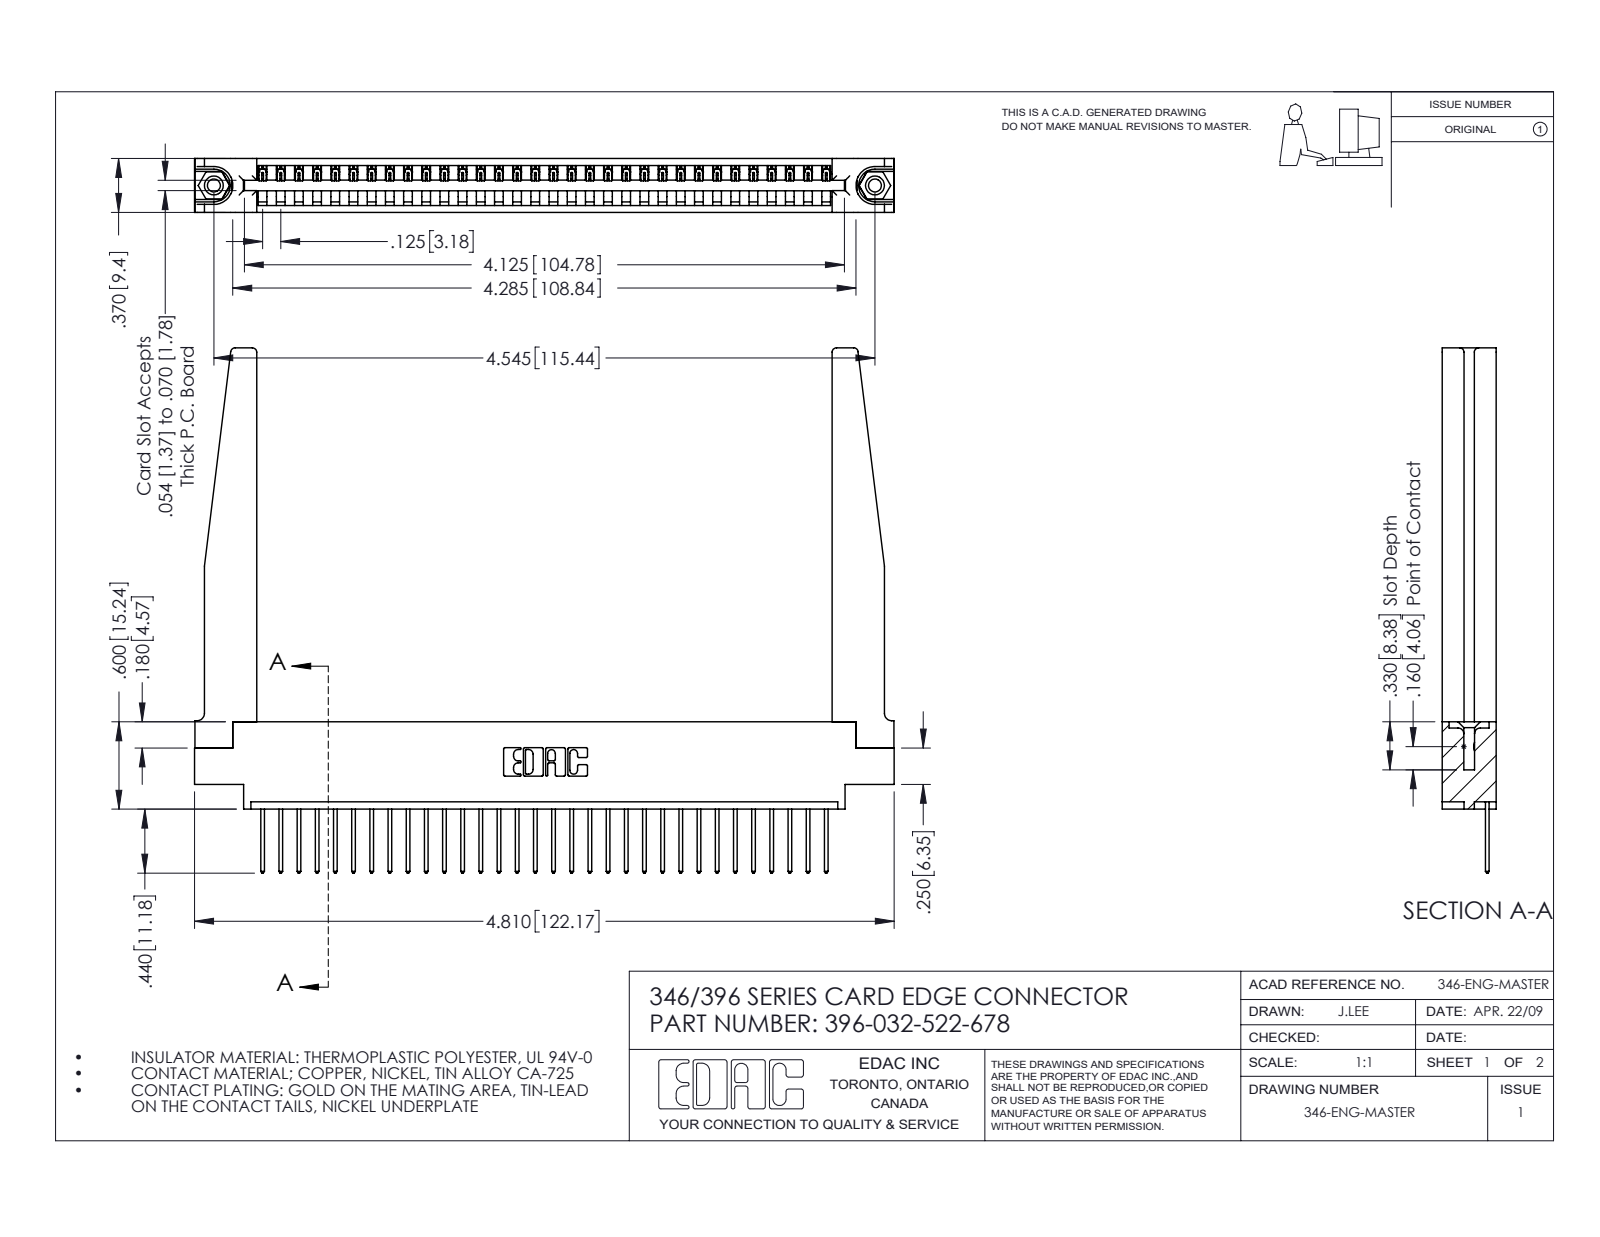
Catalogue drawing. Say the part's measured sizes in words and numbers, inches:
The part is named "396-032-522-678; 346-220-078_345-220-078; 345-250-001_345-250-001-102; 345-292-001_345-293-122 (+1 more)". Its 3-D file was written by "SolidWorks 2016 (CONFIG_CONTROL_DESIGN)". It is 37 solids with 2216 faces: 1502 planar, 662 cylindrical and 52 other. Overall it measures 4.81 by 3.61 by 0.37 inches. Its volume is 1.122 cubic inches and its surface area 32.63 square inches. Round holes: 2 of diameter 0.089, 2 of diameter 0.125, 2 of diameter 0.156, 1 of diameter 0.064. Round bosses or shafts: 2 of diameter 0.155. Partial cylindrical surfaces (rounded edges, fillets, slot ends): 64 of radius 0.006, 64 of radius 0.01, 22 of radius 0.01, 8 of radius 0.03, 6 of radius 0.007, 6 of radius 0.031, 3 of radius 0.026, 2 of radius 0.031. The main face-to-face distances are 0.37, 0.048, 0.322, 0.072, 0.148, 0.15, 0.25, 0.298, 0.025, 0.222. The hole center spacings are 0.246, 4.337, 4.545.
